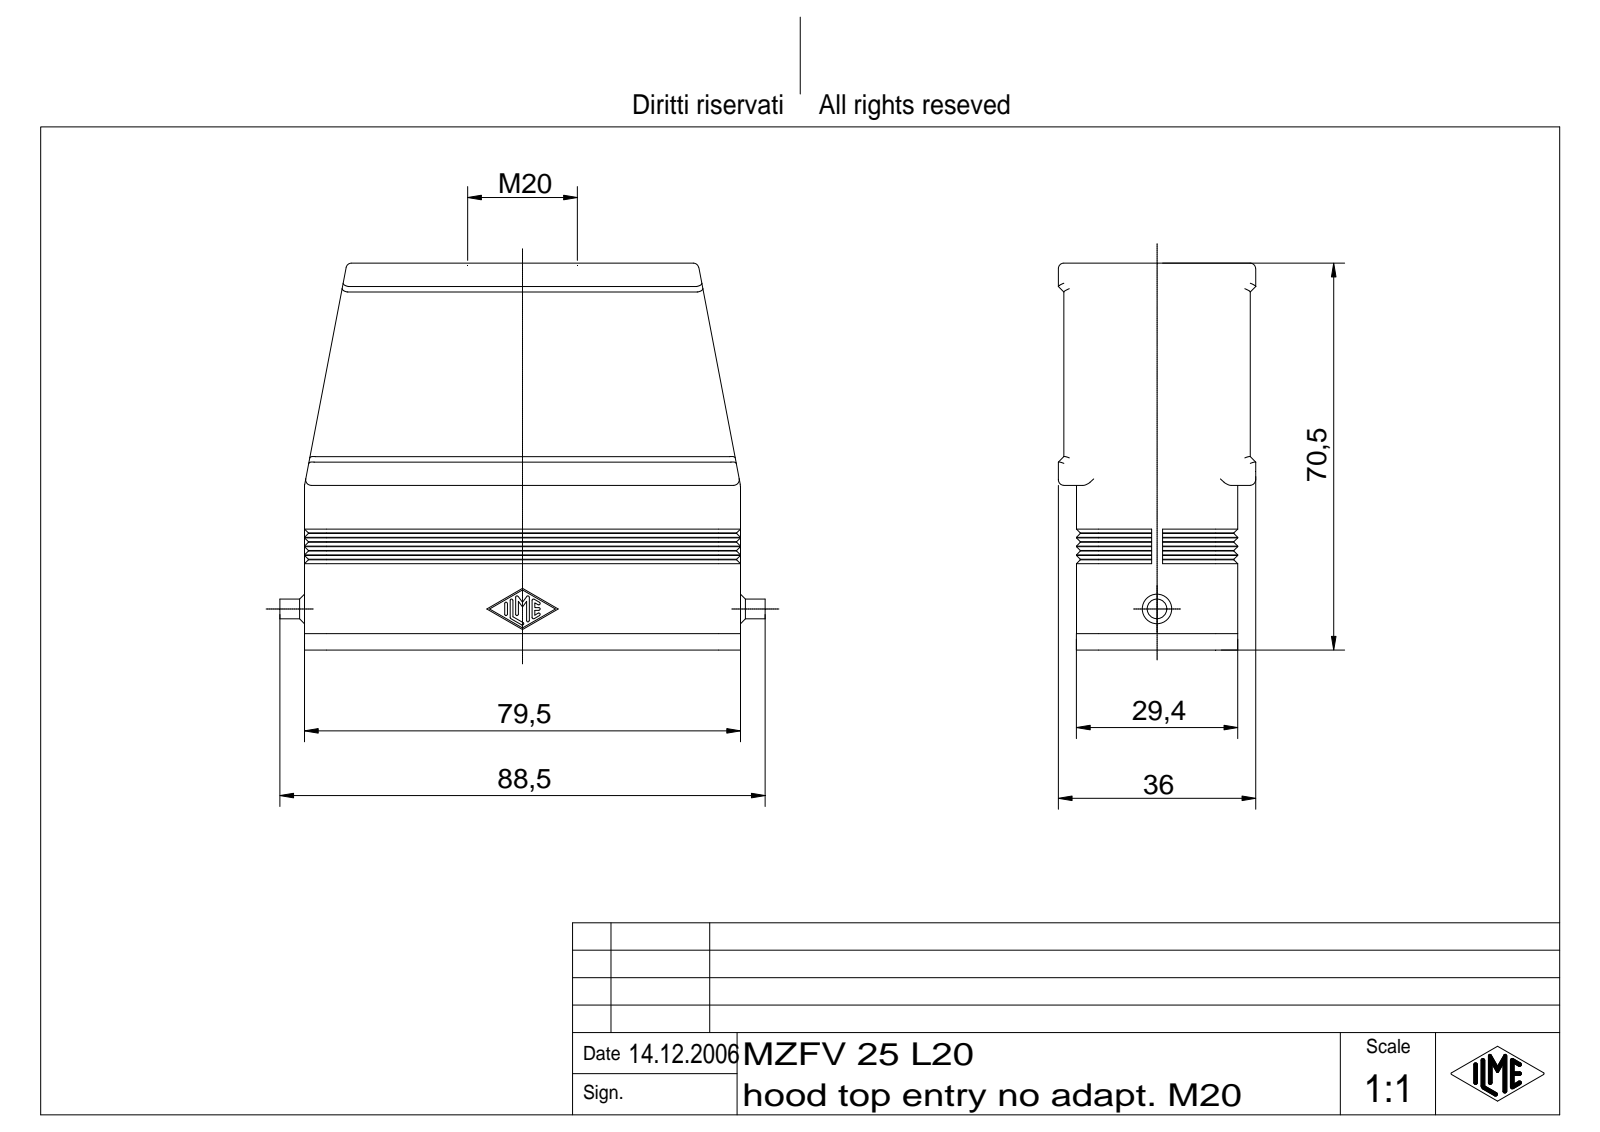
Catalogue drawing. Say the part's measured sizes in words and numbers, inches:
The part is named "CZ_MZ Tüllengehäuse 1 Bügel". Its 3-D file was written by "Autodesk Inventor 7 (AUTOMOTIVE_DESIGN)". It is 1 solid with 397 faces: 167 planar, 140 cylindrical and 90 other. Overall it measures 3.484 by 2.776 by 1.417 inches. Its volume is 4.009 cubic inches and its surface area 50.71 square inches. Round holes: 4 of diameter 0.097, 4 of diameter 0.138, 1 of diameter 0.787, 1 of diameter 0.906. Round bosses or shafts: 1 of diameter 0.142. Partial cylindrical surfaces (rounded edges, fillets, slot ends): 24 of radius 0.039, 14 of radius 0.01, 8 of radius 0.157, 6 of radius 0.079, 4 of radius 0.049, 2 of radius 0.13. The main face-to-face distances are 0.118, 0.921, 1.039, 1.13, 0.209, 0.091, 1.248, 1.157, 0.394, 0.13. The hole center spacings are 1.337, 0.63, 2.598, 2.674.
